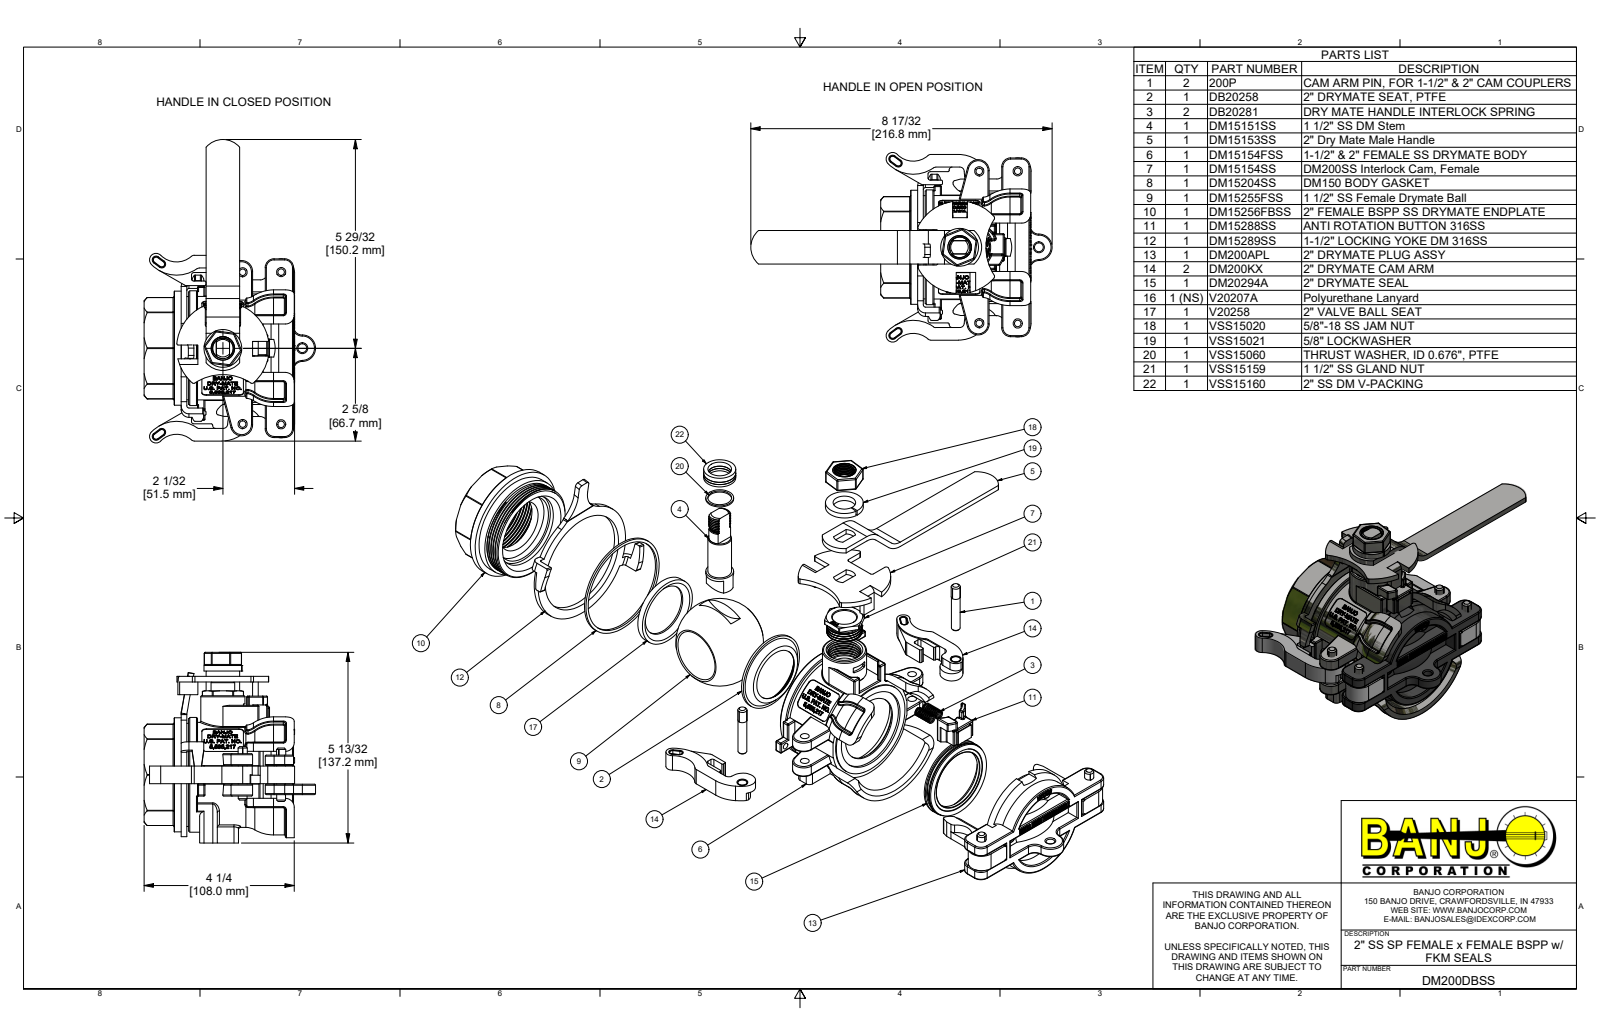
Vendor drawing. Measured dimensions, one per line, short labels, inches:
name: DM200DBSS; DM15154FSS; DB20258; DB20281 (+8 more)
written by: Autodesk Inventor 2022 (AUTOMOTIVE_DESIGN)
unit: in
bodies: 35 solids, 3049 faces (1195 planar, 741 cylindrical, 1113 other)
size: 13.635 × 5.915 × 5.406
volume: 28.66 in³; area: 338 in²
holes: 5× ⌀0.25, 4× ⌀0.256, 3× ⌀0.125, 2× ⌀1.5, 1× ⌀0.18, 1× ⌀0.64, 1× ⌀0.662, 1× ⌀0.67, 1× ⌀0.676, 1× ⌀0.69, 1× ⌀0.84, 1× ⌀0.876
bosses: 4× ⌀0.26, 4× ⌀0.249, 3× ⌀0.28, 1× ⌀3.5, 1× ⌀3.23, 1× ⌀3.19, 1× ⌀2.975, 1× ⌀2.97
rounds: 178× R0.03, 25× R0.06, 10× R0.12, 10× R0.125, 10× R0.25, 9× R0.08, 6× R0.032, 6× R1
face distances: 0.298, 0.16, 0.15, 0.85, 1.68, 2.18, 0.86, 0.86, 0.31, 0.81
hole spacings: 0.95, 1.09, 1.646, 2.222, 2.237, 2.249, 2.713, 2.735
